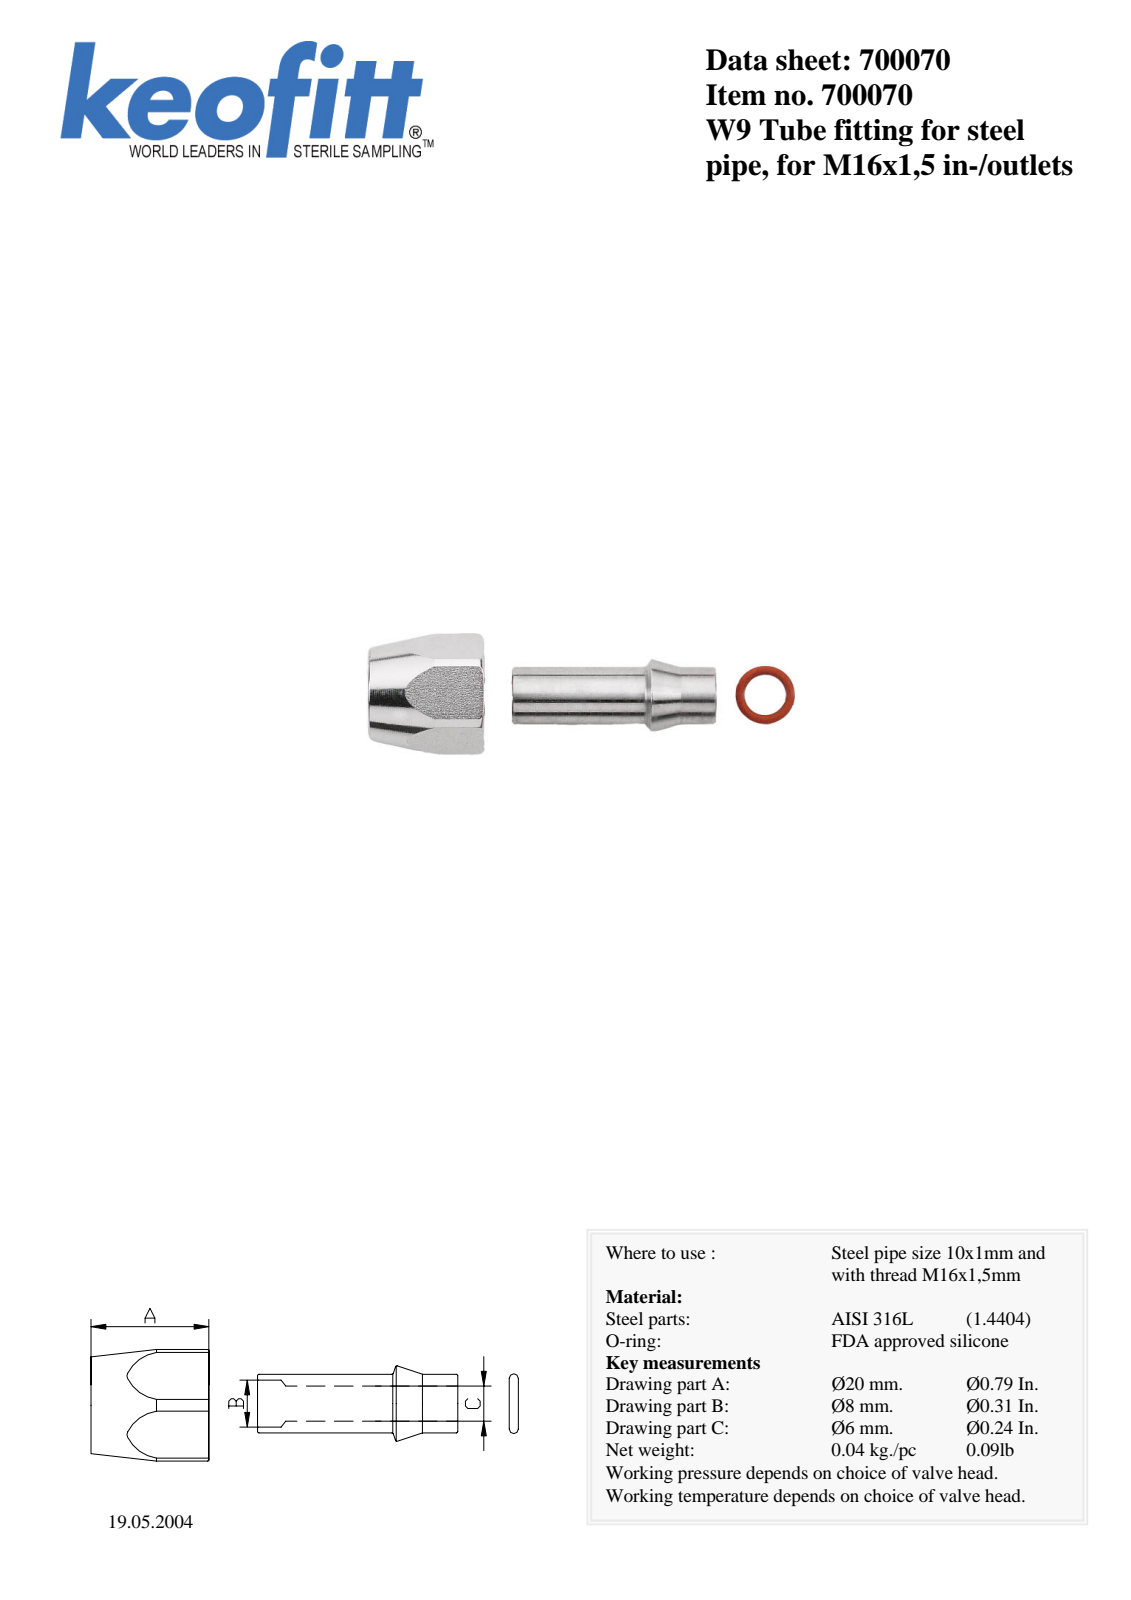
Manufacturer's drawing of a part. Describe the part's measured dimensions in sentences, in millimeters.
The part is named "700070_simplify". Its 3-D file was written by "Autodesk Inventor 2022 (AUTOMOTIVE_DESIGN)". It is 2 solids with 31 faces: 11 planar, 8 cylindrical and 12 other. Overall it measures 36.6 by 21 by 19 millimeters. Its volume is 6 841 cubic millimeters and its surface area 2 296 square millimeters. Round bosses or shafts: 1 of diameter 10. Partial cylindrical surfaces (rounded edges, fillets, slot ends): 1 of radius 10.5. The main face-to-face distances are 19, 20, 14.5, 34.5, 35, 20.5, 0.5.
